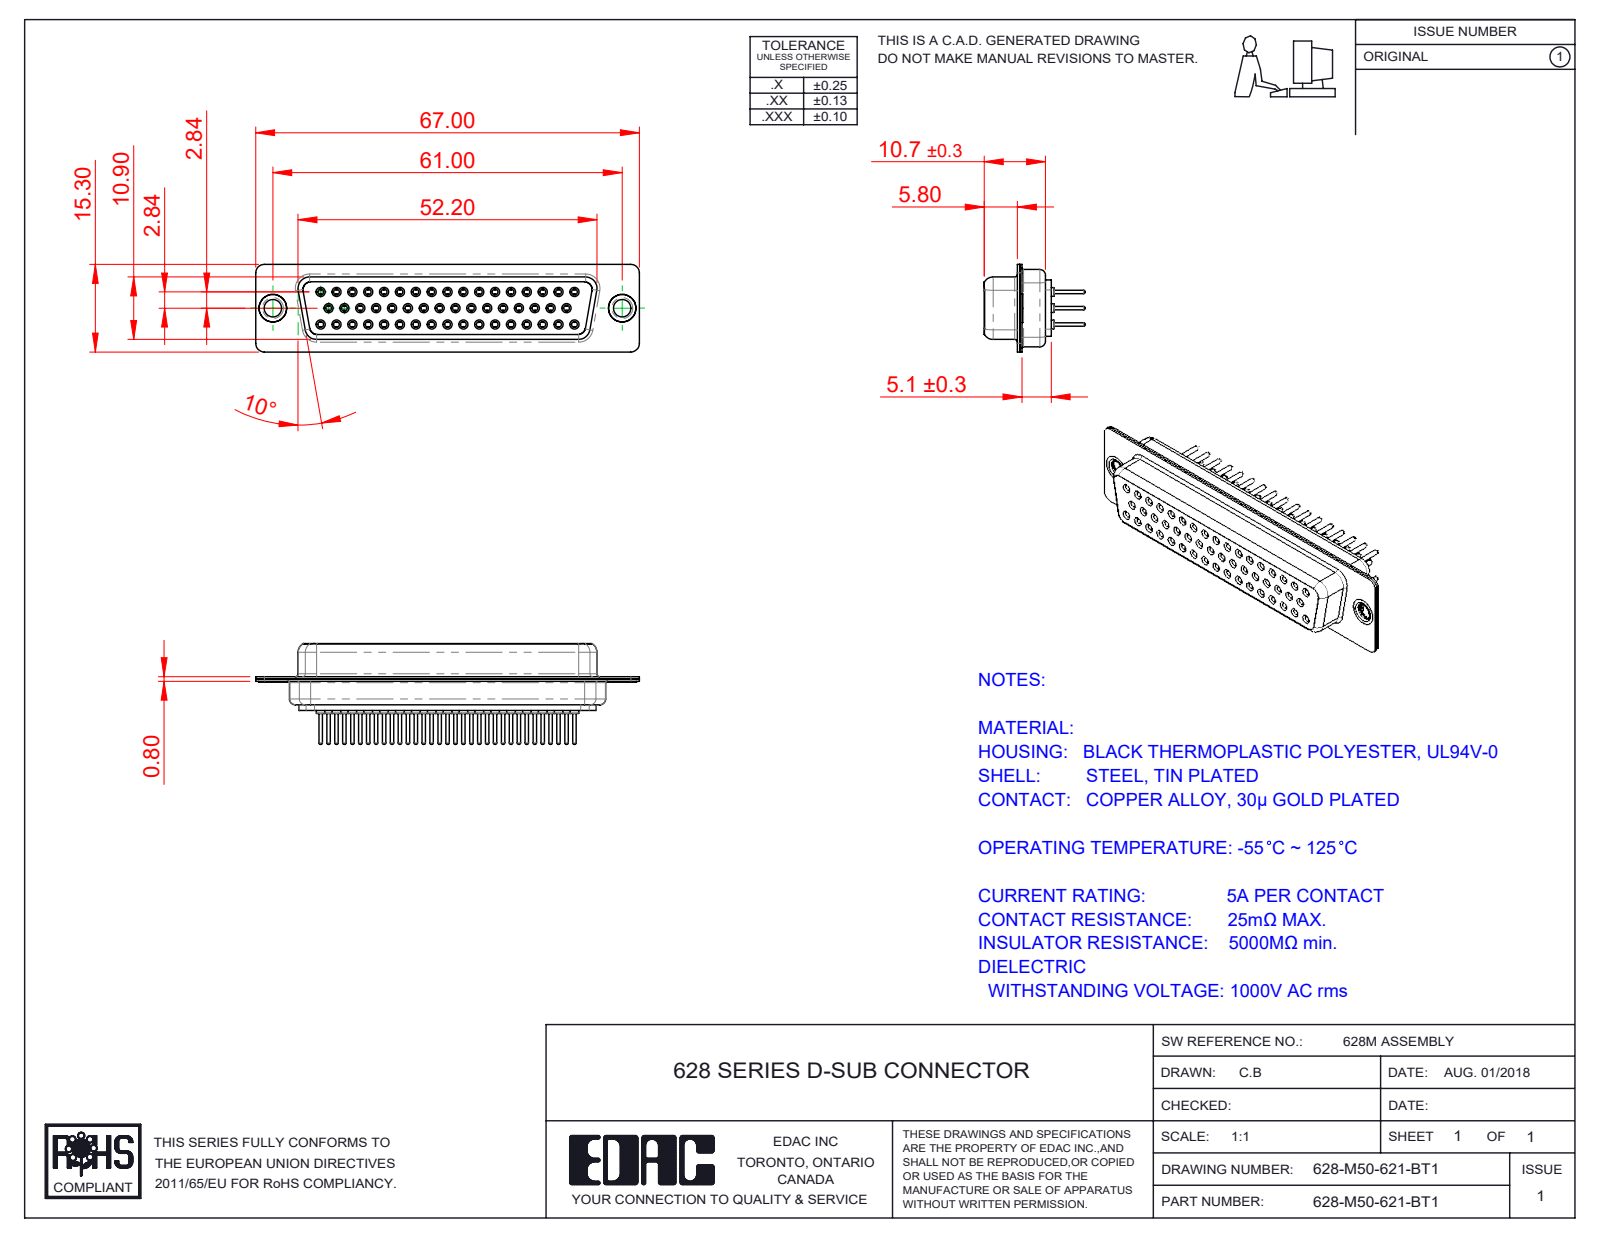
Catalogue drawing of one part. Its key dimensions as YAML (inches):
part_name: "628-M50-621-BT1; 628M Shell Rear_50 Contacts; 628M Thru Hole Rivet; 628M Housing_50 Contacts (+4 more)"
step_written_by: "SolidWorks 2020 (CONFIG_CONTROL_DESIGN)"
units: inches
bodies: {solids: 55, faces: 3003, planar: 817, cylindrical: 1071, other: 1115}
overall_size: [2.638, 0.693, 0.602]
volume: 0.399
surface_area: 23.08
round_holes:
  - {diameter: 0.039, count: 50}
  - {diameter: 0.043, count: 50}
  - {diameter: 0.067, count: 50}
  - {diameter: 0.071, count: 50}
  - {diameter: 0.079, count: 50}
  - {diameter: 0.12, count: 2}
  - {diameter: 0.157, count: 2}
  - {diameter: 0.189, count: 2}
round_bosses_or_shafts:
  - {diameter: 0.087, count: 50}
  - {diameter: 0.063, count: 50}
  - {diameter: 0.059, count: 50}
  - {diameter: 0.024, count: 50}
  - {diameter: 0.197, count: 2}
  - {diameter: 0.193, count: 2}
  - {diameter: 0.14, count: 2}
partial_cylinders:
  - {radius: 0.059, count: 16}
  - {radius: 0.079, count: 12}
  - {radius: 0.053, count: 8}
  - {radius: 0.063, count: 8}
  - {radius: 0.01, count: 4}
  - {radius: 0.02, count: 4}
  - {radius: 0.024, count: 4}
  - {radius: 0.026, count: 4}
face_to_face_distances: [0.016, 0.051, 0.465, 0.035, 0.217, 0.232, 0.033, 0.516, 0.228, 0.396]
hole_center_spacings: [0.124, 0.109, 0.218, 0.327, 0.436, 0.545, 0.654, 0.763]
